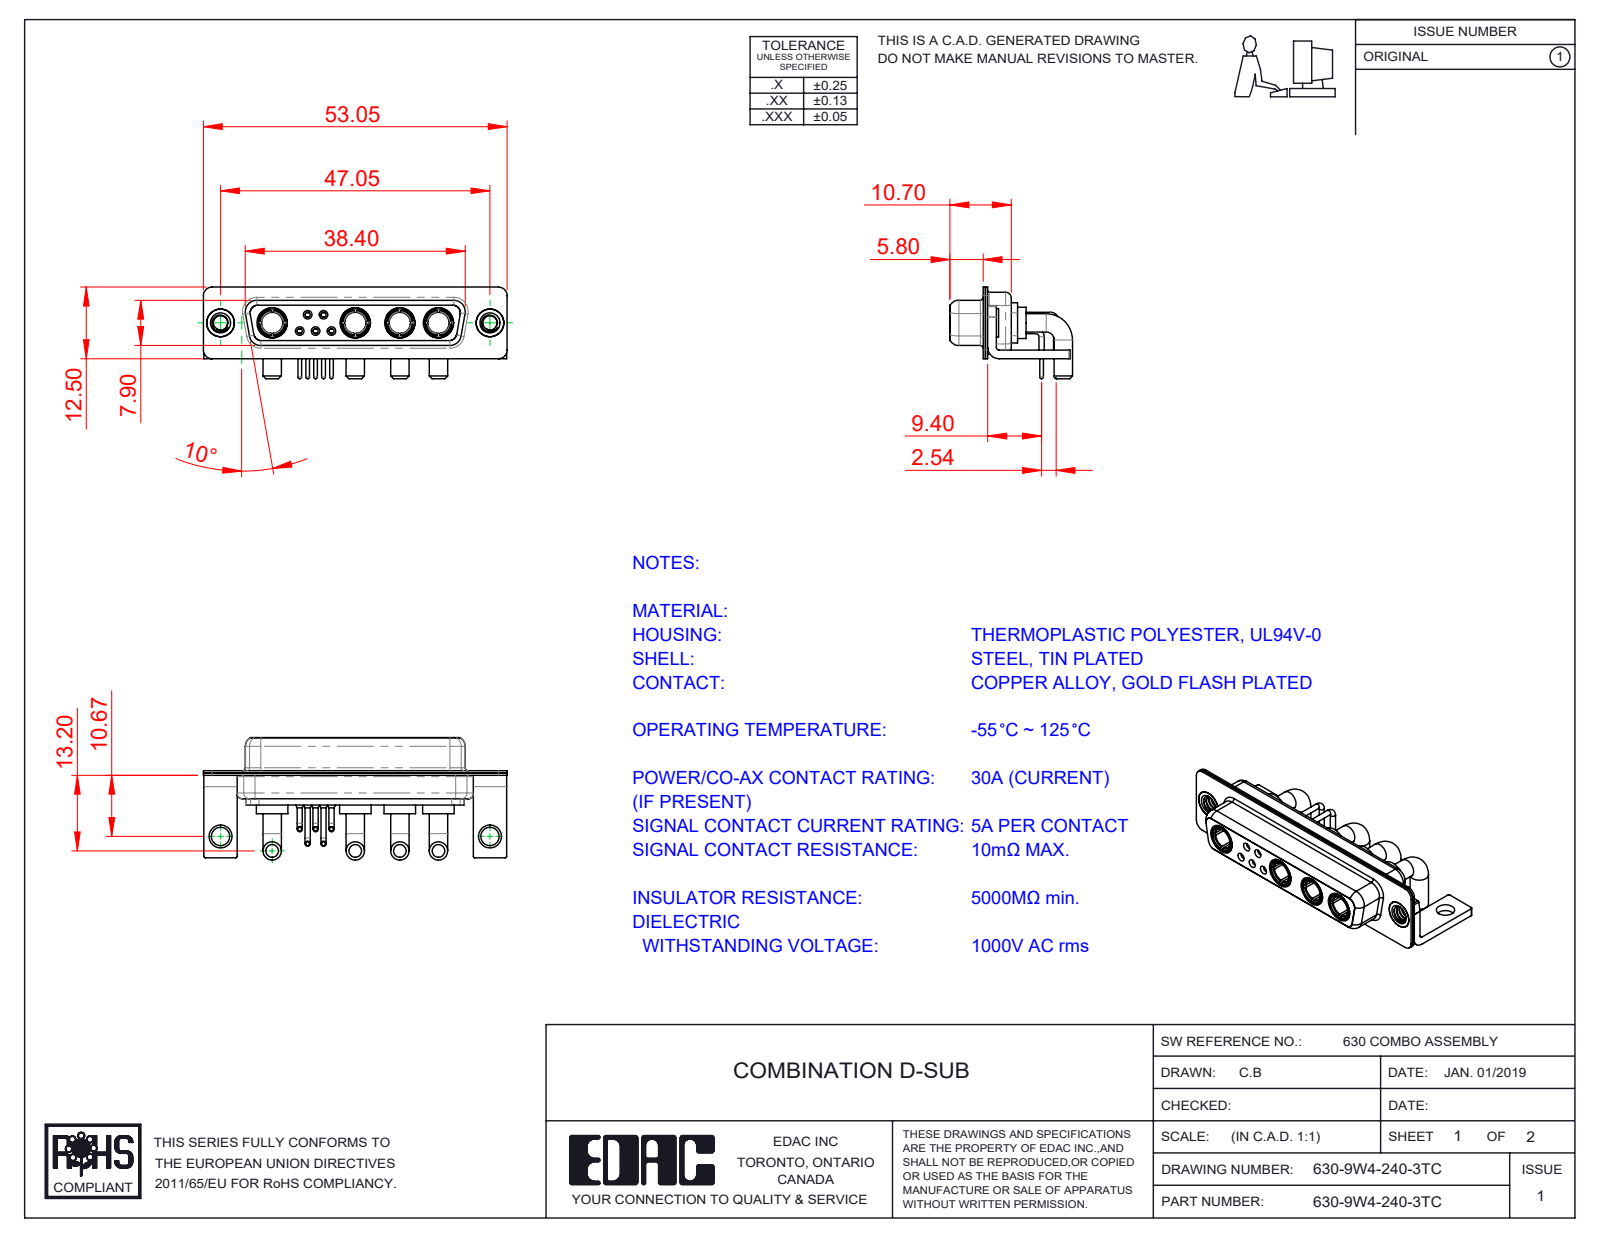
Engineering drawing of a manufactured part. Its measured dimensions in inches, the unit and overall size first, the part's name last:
Units: inches
Overall size (bounding box): 2.089 × 0.843 × 0.63
Round holes (diameter × count): ⌀0.191 ×6, ⌀0.035 ×5, ⌀0.043 ×5, ⌀0.059 ×5, ⌀0.079 ×5, ⌀0.146 ×4, ⌀0.209 ×4, ⌀0.063 ×3, ⌀0.067 ×2, ⌀0.098 ×2, ⌀0.126 ×2, ⌀0.157 ×2
Round bosses / shafts (diameter × count): ⌀0.126 ×8, ⌀0.035 ×5, ⌀0.026 ×5, ⌀0.217 ×4, ⌀0.205 ×4, ⌀0.195 ×4, ⌀0.187 ×4, ⌀0.148 ×4
Partial cylindrical surfaces — rounded edges, fillets, slot ends (radius × count): R0.01 ×16, R0.059 ×16, R0.079 ×13, R0.053 ×8, R0.063 ×8, R0.02 ×5, R0.024 ×4, R0.026 ×4
Main face-to-face distances: 0.016, 0.018, 0.055, 0.333, 0.071, 0.031, 0.35, 0.244, 0.059, 0.278
Hole centre spacings: 0.124, 0.109, 1.852, 0.173, 0.198, 0.198, 0.198, 0.218
Volume: 0.268 in³ · Surface area: 14.74 in²
Bodies: 20 solids, 894 faces (278 planar, 370 cylindrical, 246 other)
Part name (STEP PRODUCT): Power Socket_30A RA; 630Combo Shell Rear_25 Contacts; 630Combo Contact Row 1; 630Combo Shell Front_25 Contacts (+5 more)
STEP written by: SolidWorks 2020 (CONFIG_CONTROL_DESIGN)
